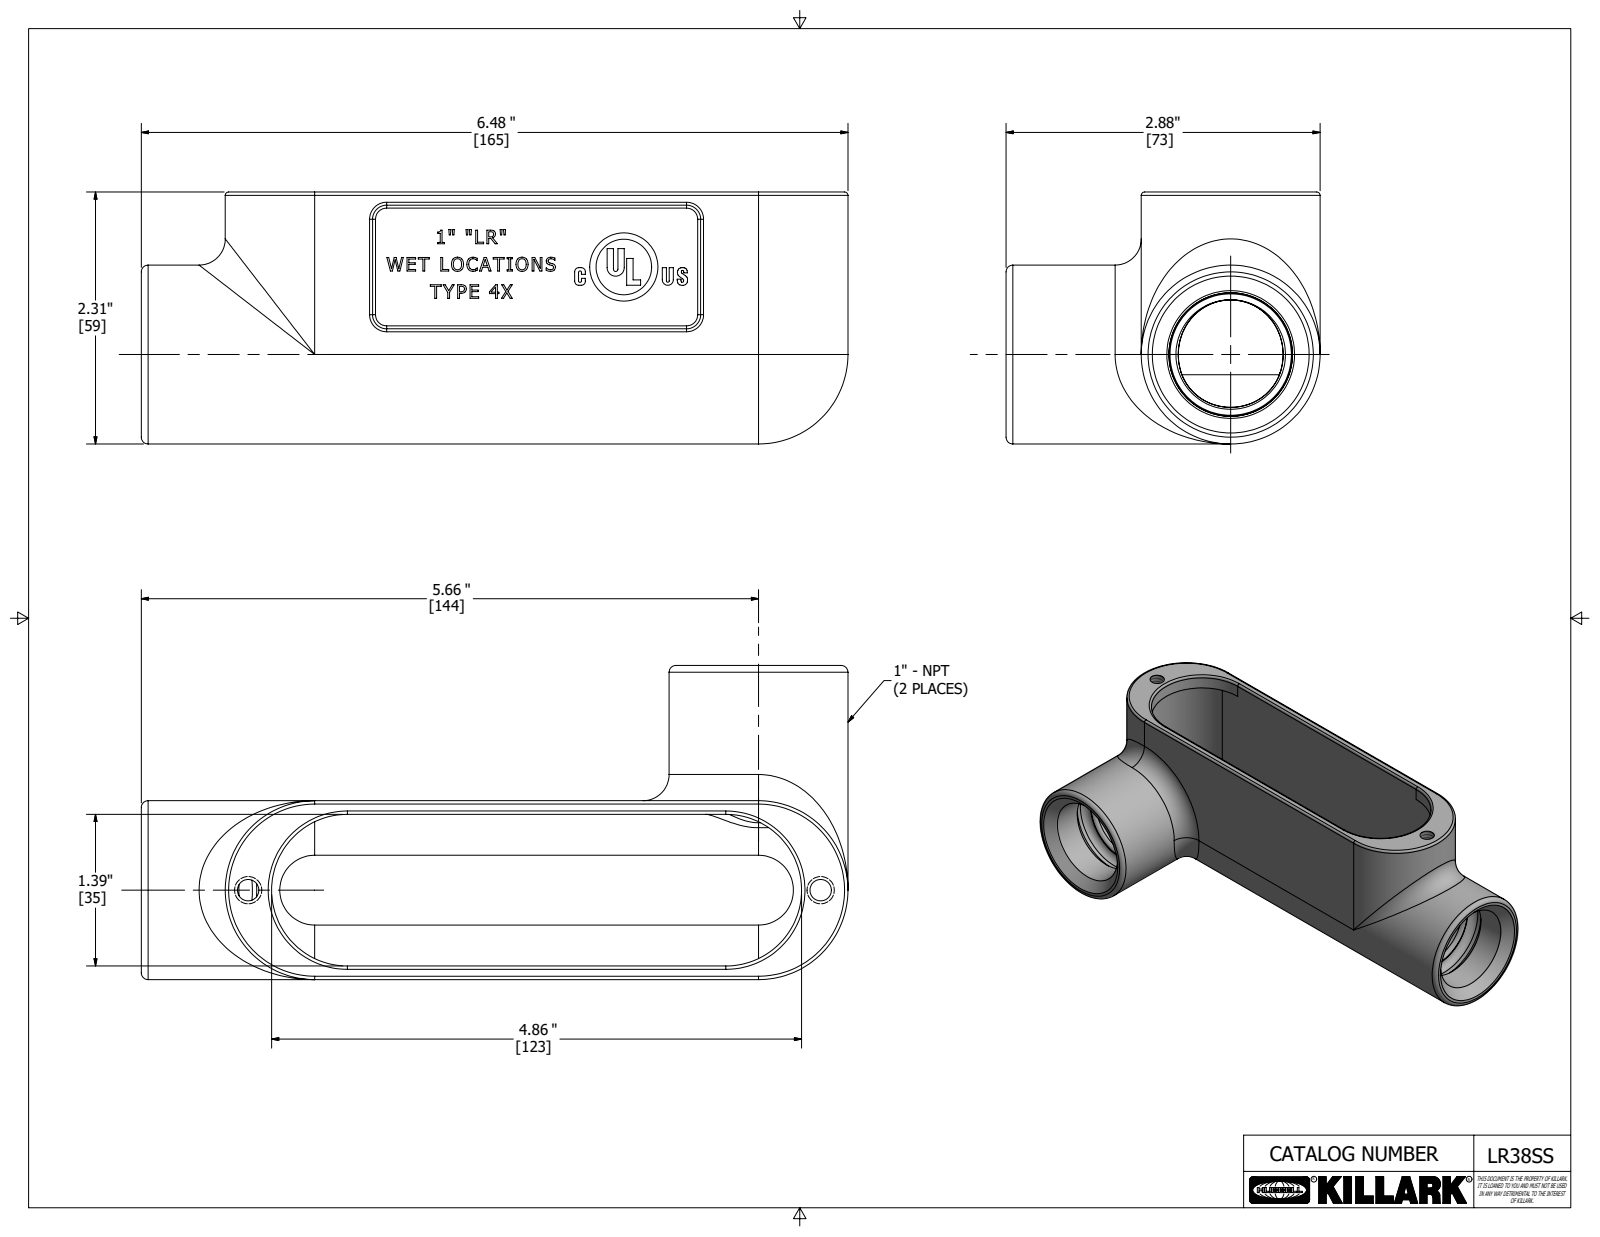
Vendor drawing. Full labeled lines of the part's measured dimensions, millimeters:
Part name (STEP PRODUCT): LR38SS
STEP written by: Autodesk Inventor 2020 (AUTOMOTIVE_DESIGN)
Units: millimetres
Bodies: 1 solid, 474 faces (289 planar, 67 cylindrical, 118 other)
Overall size (bounding box): 164.6 × 73.2 × 58.7
Volume: 112 000 mm³ · Surface area: 55 700 mm²
Round holes (diameter × count): ⌀5 ×2, ⌀33.6 ×2, ⌀12.9 ×1
Round bosses / shafts (diameter × count): ⌀41.7 ×2, ⌀15.9 ×1
Partial cylindrical surfaces — rounded edges, fillets, slot ends (radius × count): R0.8 ×9, R0.8 ×4, R1 ×4, R17.7 ×4, R0.3 ×2, R0.3 ×2, R9.5 ×2, R20.8 ×2
Main face-to-face distances: 3.2, 38.5, 35.3, 40.9, 37.7, 2.4, 41.7, 0.8, 52.1, 47
Hole centre spacings: 37.4, 133.4
